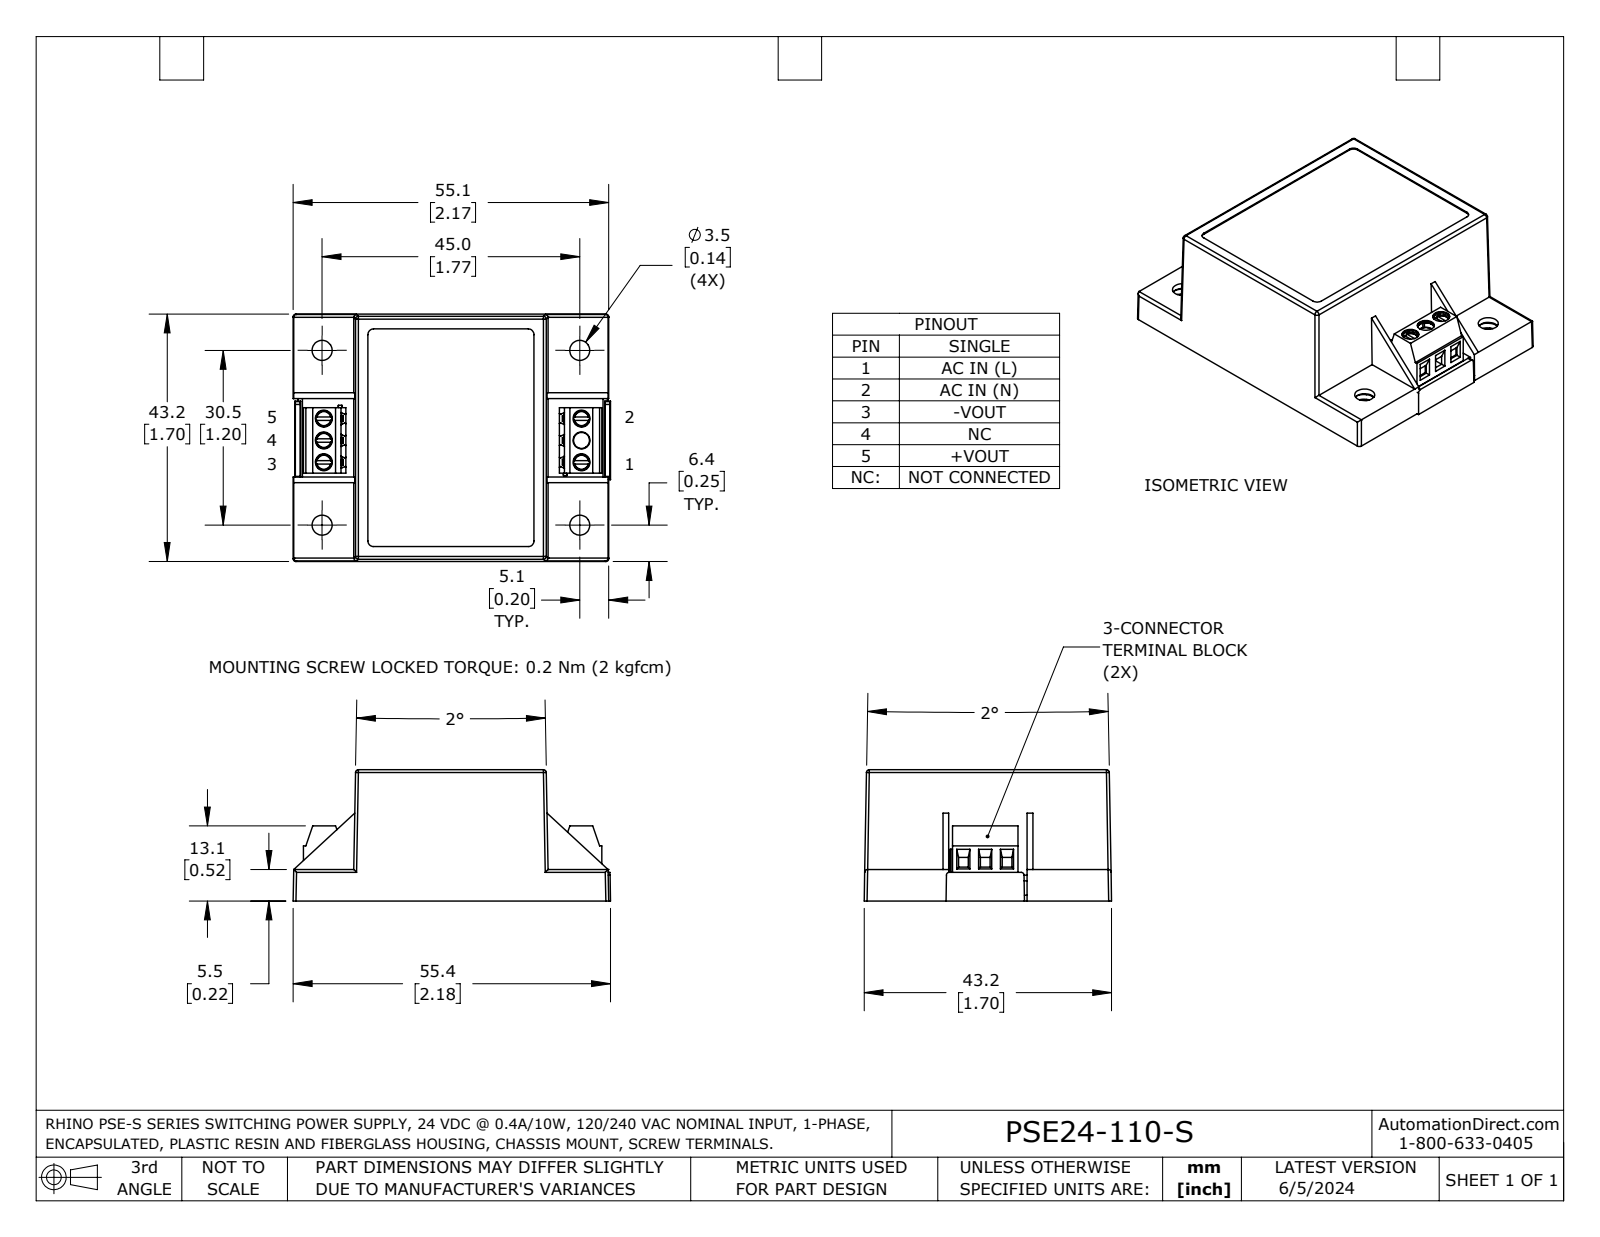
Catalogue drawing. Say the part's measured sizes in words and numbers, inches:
The part is named "PSE24-110-S". Its 3-D file was written by "SolidWorks 2023 (AUTOMOTIVE_DESIGN)". It is 5 solids with 655 faces: 491 planar, 130 cylindrical and 34 other. Overall it measures 2.005 by 1.708 by 1.701 inches. Its volume is 0.65 cubic inches and its surface area 34.63 square inches. Round holes: 8 of diameter 0.138, 6 of diameter 0.116, 4 of diameter 0.161, 1 of diameter 0.11. Partial cylindrical surfaces (rounded edges, fillets, slot ends): 19 of radius 0.02, 18 of radius 0.009, 12 of radius 0.006, 8 of radius 0.004, 4 of radius 0.008, 4 of radius 0.01, 4 of radius 0.039, 4 of radius 0.079. The main face-to-face distances are 0.039, 0.138, 0.855, 0.717, 0.177, 0.098, 0.815, 0.678, 0.894, 0.756. The hole center spacings are 1.772, 0.022, 0.15, 0.45, 0.6, 0.75, 1.201, 1.778.
